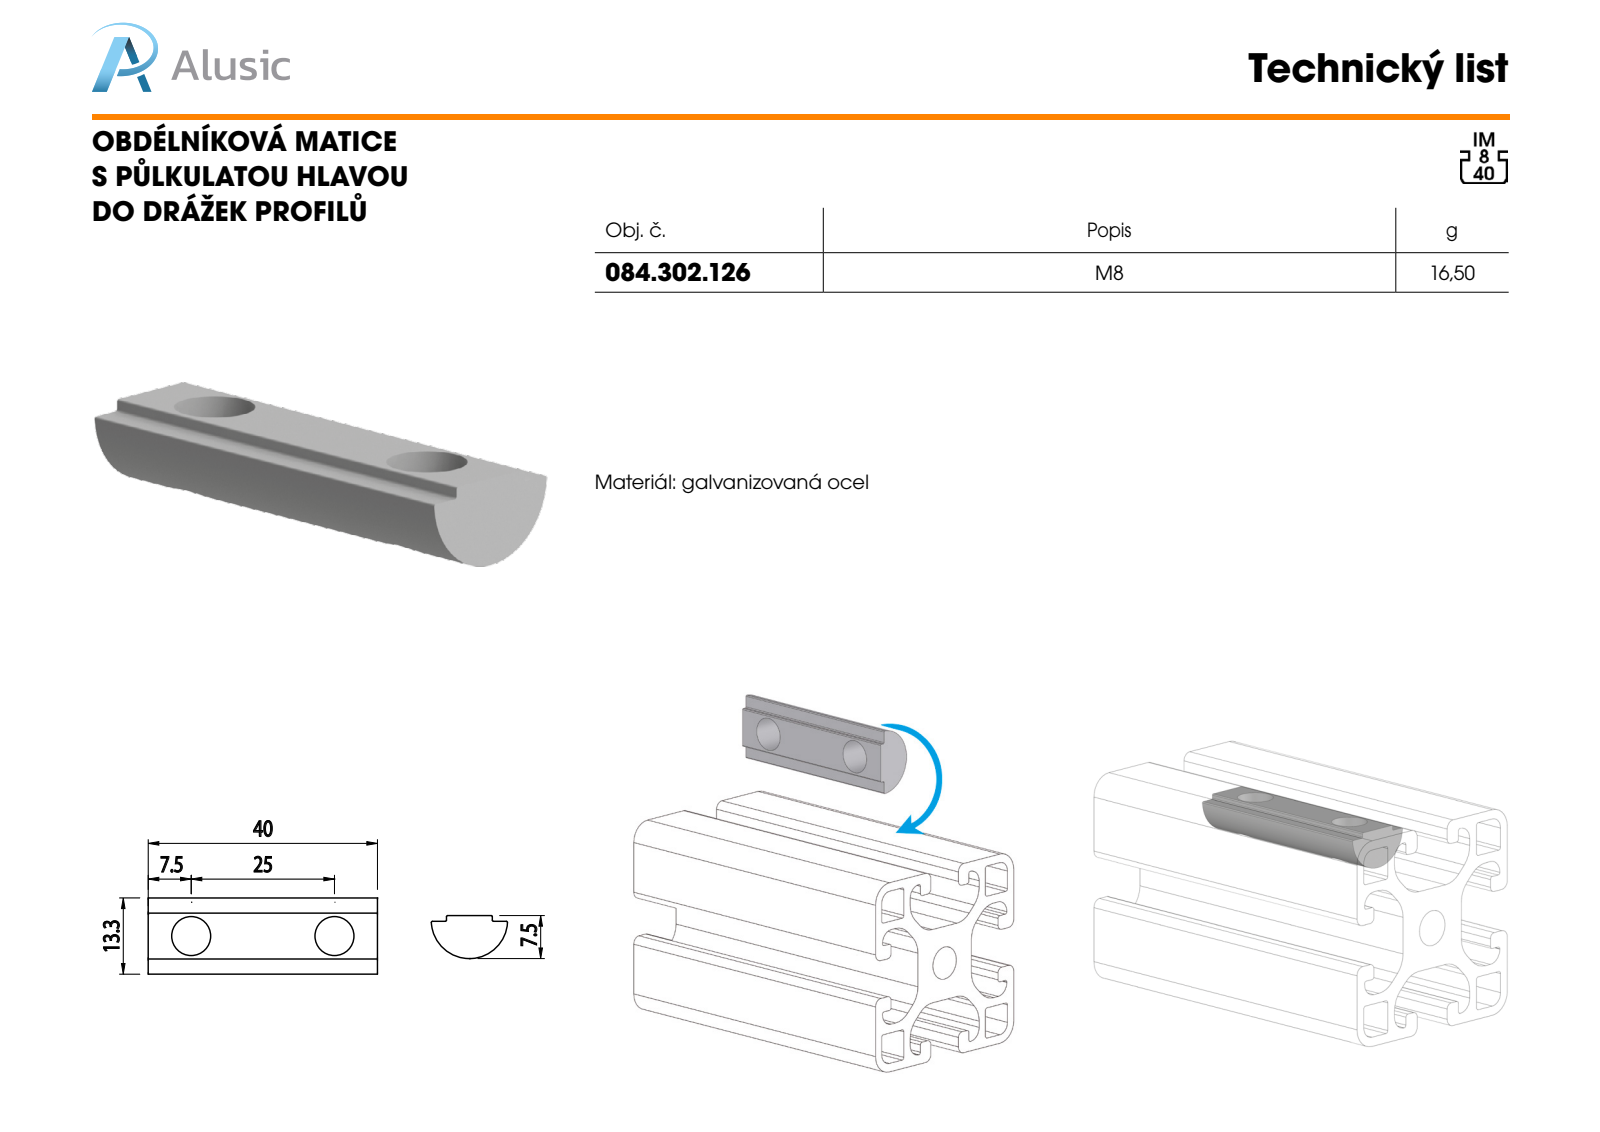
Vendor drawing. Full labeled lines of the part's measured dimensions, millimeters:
Part name (STEP PRODUCT): 084.302.126
STEP written by: SolidWorks 2016 (CONFIG_CONTROL_DESIGN)
Units: millimetres
Bodies: 1 solid, 19 faces (7 planar, 12 cylindrical, 0 other)
Overall size (bounding box): 40 × 13.28 × 7.5
Volume: 2 490 mm³ · Surface area: 1 718 mm²
Round holes (diameter × count): ⌀6.8 ×2
Partial cylindrical surfaces — rounded edges, fillets, slot ends (radius × count): R0.2 ×6, R6.65 ×1
Main face-to-face distances: 1, 40, 8
Hole centre spacings: 25
